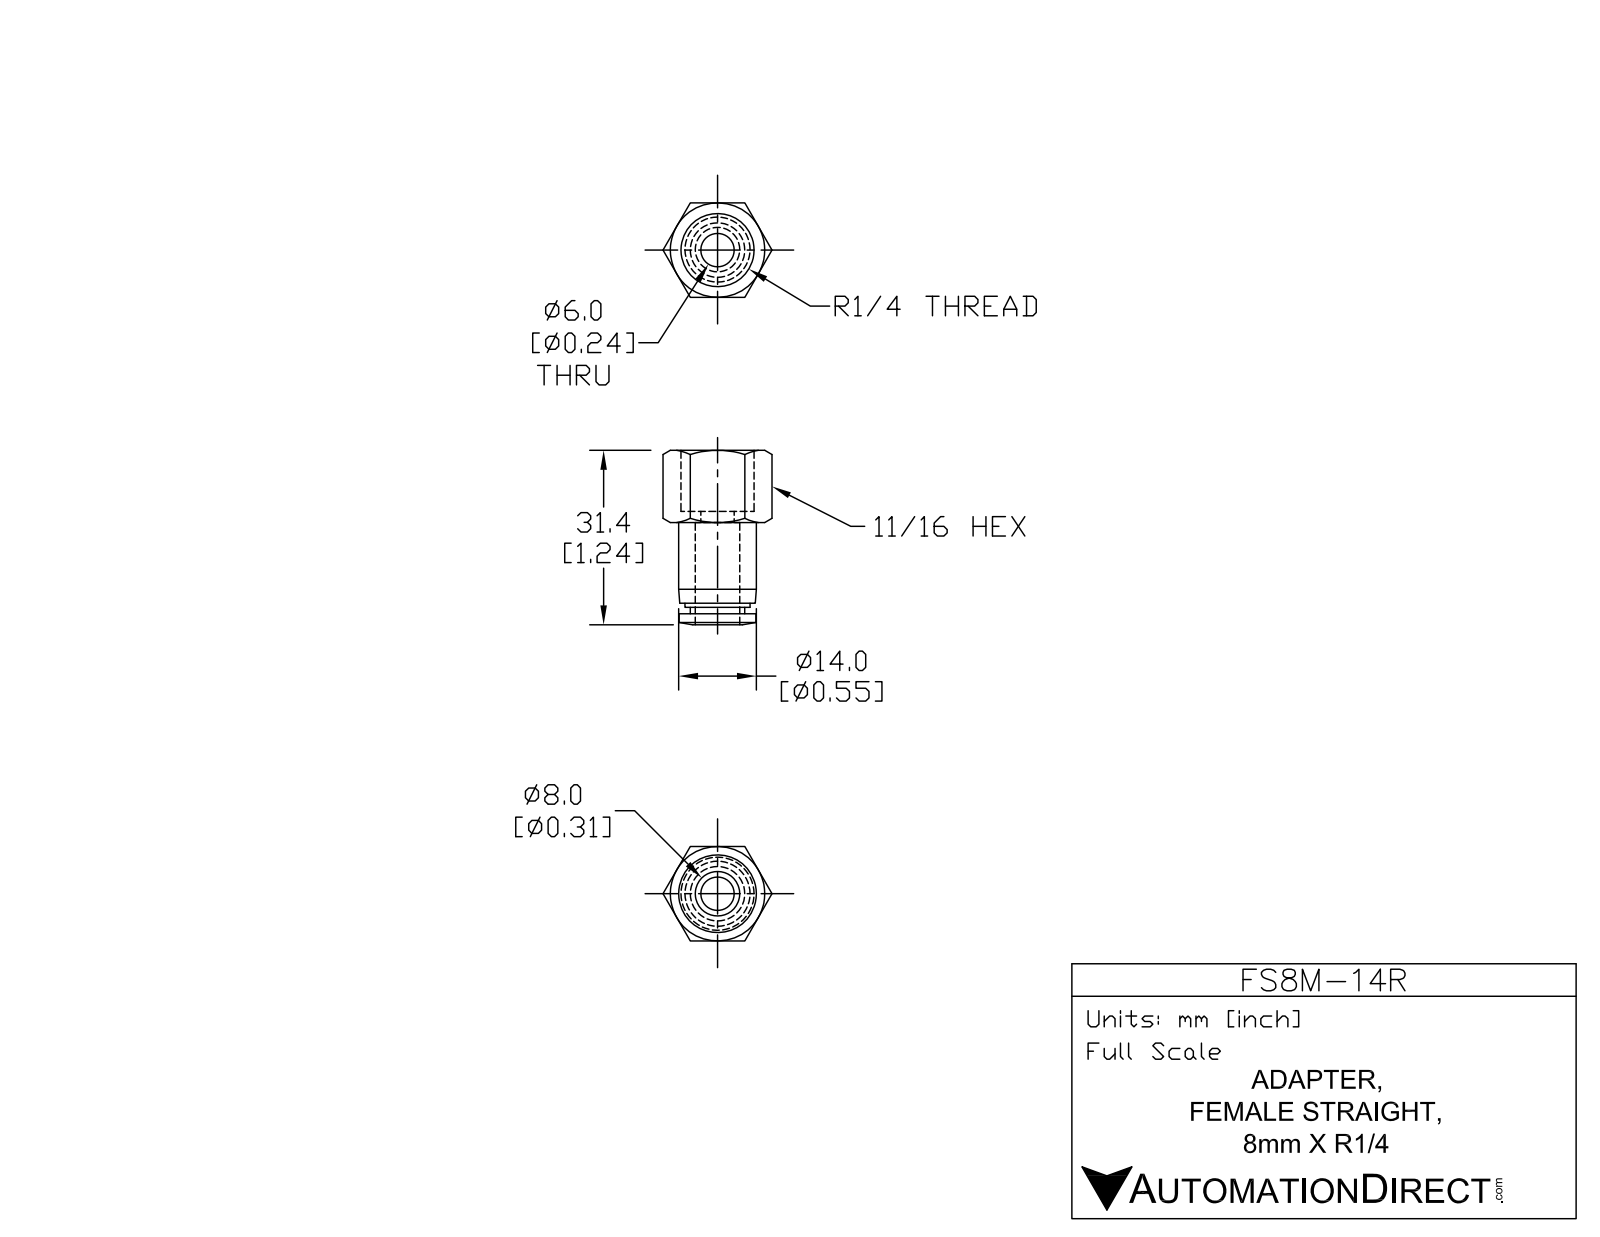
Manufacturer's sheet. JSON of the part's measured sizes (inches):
{"part_name": "FS8M-14R", "step_written_by": "SolidWorks 2015 (AUTOMOTIVE_DESIGN)", "units": "inches", "bodies": {"solids": 1, "faces": 48, "planar": 14, "cylindrical": 12, "other": 22}, "overall_size": [1.236, 0.773, 0.669], "volume_in3": 0.21, "surface_area_in2": 4.711, "round_holes": [[0.236, 1], [0.327, 1]], "round_bosses_or_shafts": [[0.551, 1], [0.543, 1], [0.461, 1], [0.386, 1]], "face_to_face_distances": [0.669, 0.079, 0.433, 0.512, 0.724, 1.157, 0.646, 1.083, 0.65, 0.571]}
